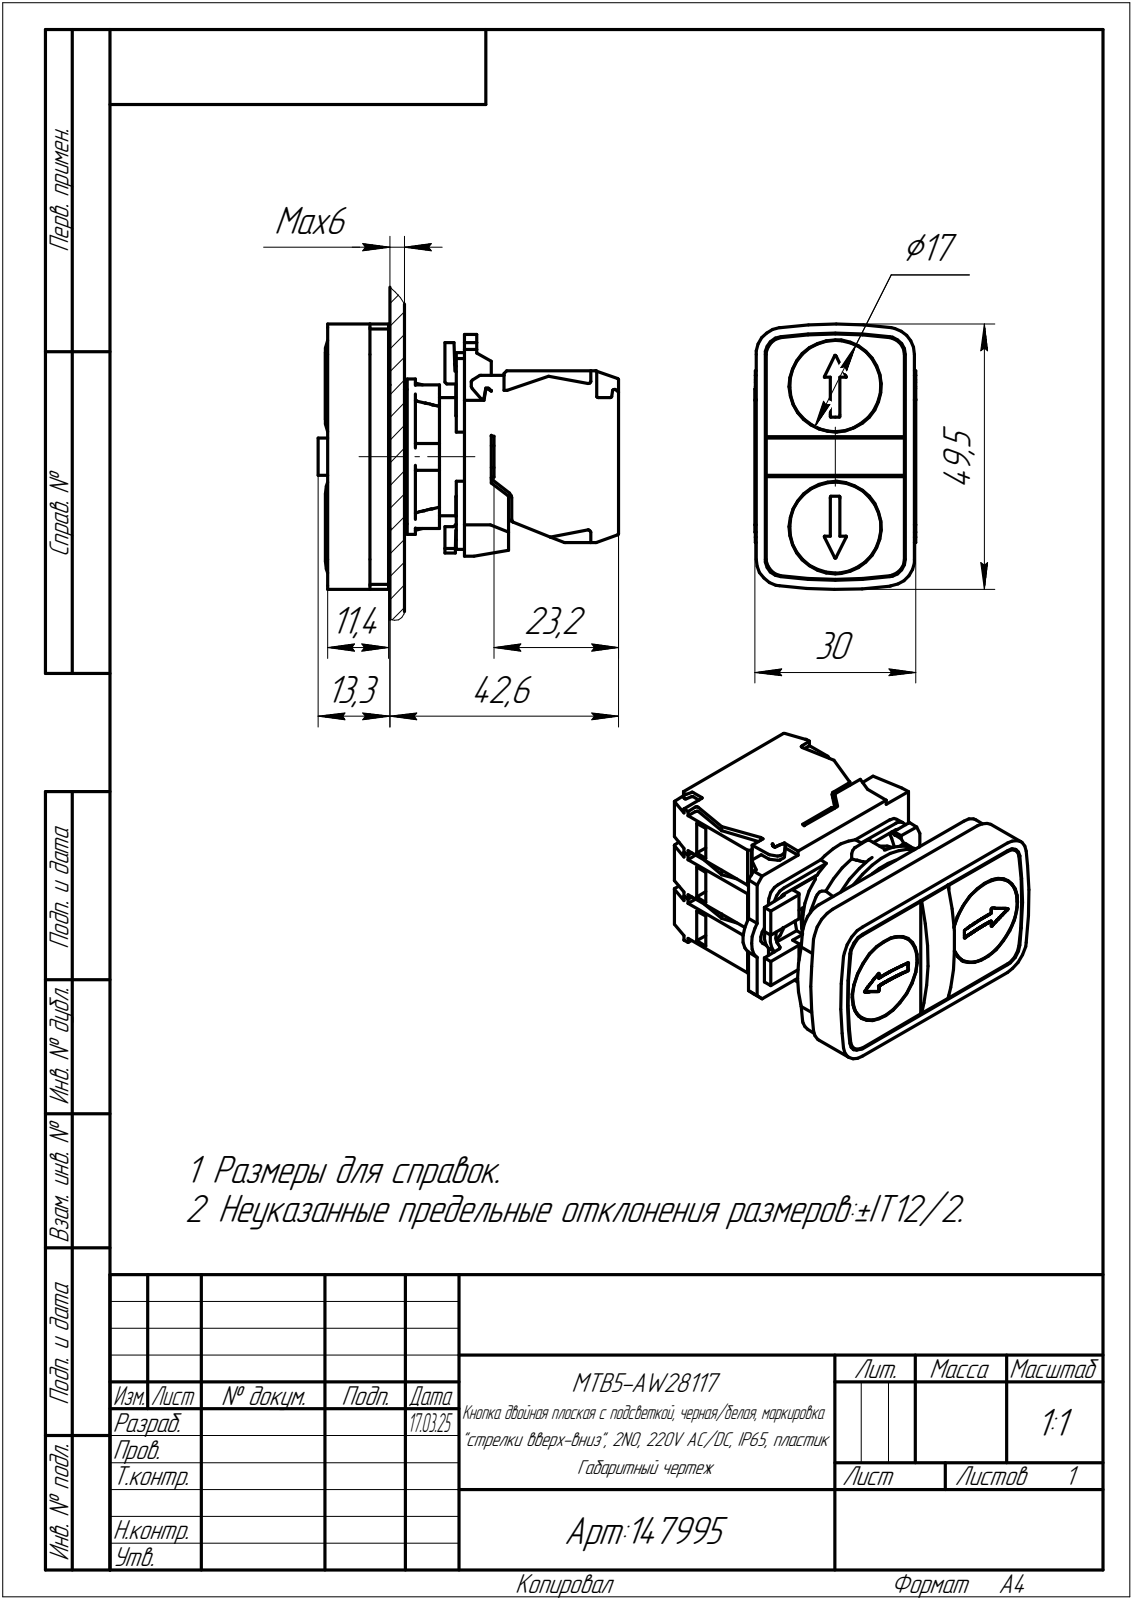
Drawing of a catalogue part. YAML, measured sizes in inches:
part_name: "LA167-B5-AWA2812315-24V"
step_written_by: "PRO/ENGINEER BY PARAMETRIC TECHNOLOGY CORPORATION, 2010280 (CONFIG_CONTROL_DESIGN)"
units: inches
bodies: {solids: 1, faces: 676, planar: 451, cylindrical: 200, other: 25}
overall_size: [2.201, 1.949, 1.181]
volume: 2.913
surface_area: 30.08
round_holes:
  - {diameter: 0.236, count: 2}
  - {diameter: 0.677, count: 2}
  - {diameter: 0.205, count: 1}
  - {diameter: 0.807, count: 1}
round_bosses_or_shafts:
  - {diameter: 0.669, count: 2}
  - {diameter: 1.142, count: 1}
  - {diameter: 1.055, count: 1}
  - {diameter: 0.984, count: 1}
  - {diameter: 0.866, count: 1}
partial_cylinders:
  - {radius: 0.039, count: 15}
  - {radius: 0.008, count: 13}
  - {radius: 0.004, count: 10}
  - {radius: 0.02, count: 7}
  - {radius: 0.098, count: 4}
  - {radius: 0.122, count: 4}
  - {radius: 0.13, count: 4}
  - {radius: 0.171, count: 4}
face_to_face_distances: [0.394, 0.39, 0.787, 0.783, 0.398, 0.555, 0.354, 1.004, 0.449, 0.752]
hole_center_spacings: [0.185, 0.335, 0.52, 0.854, 0.669, 1.039]
